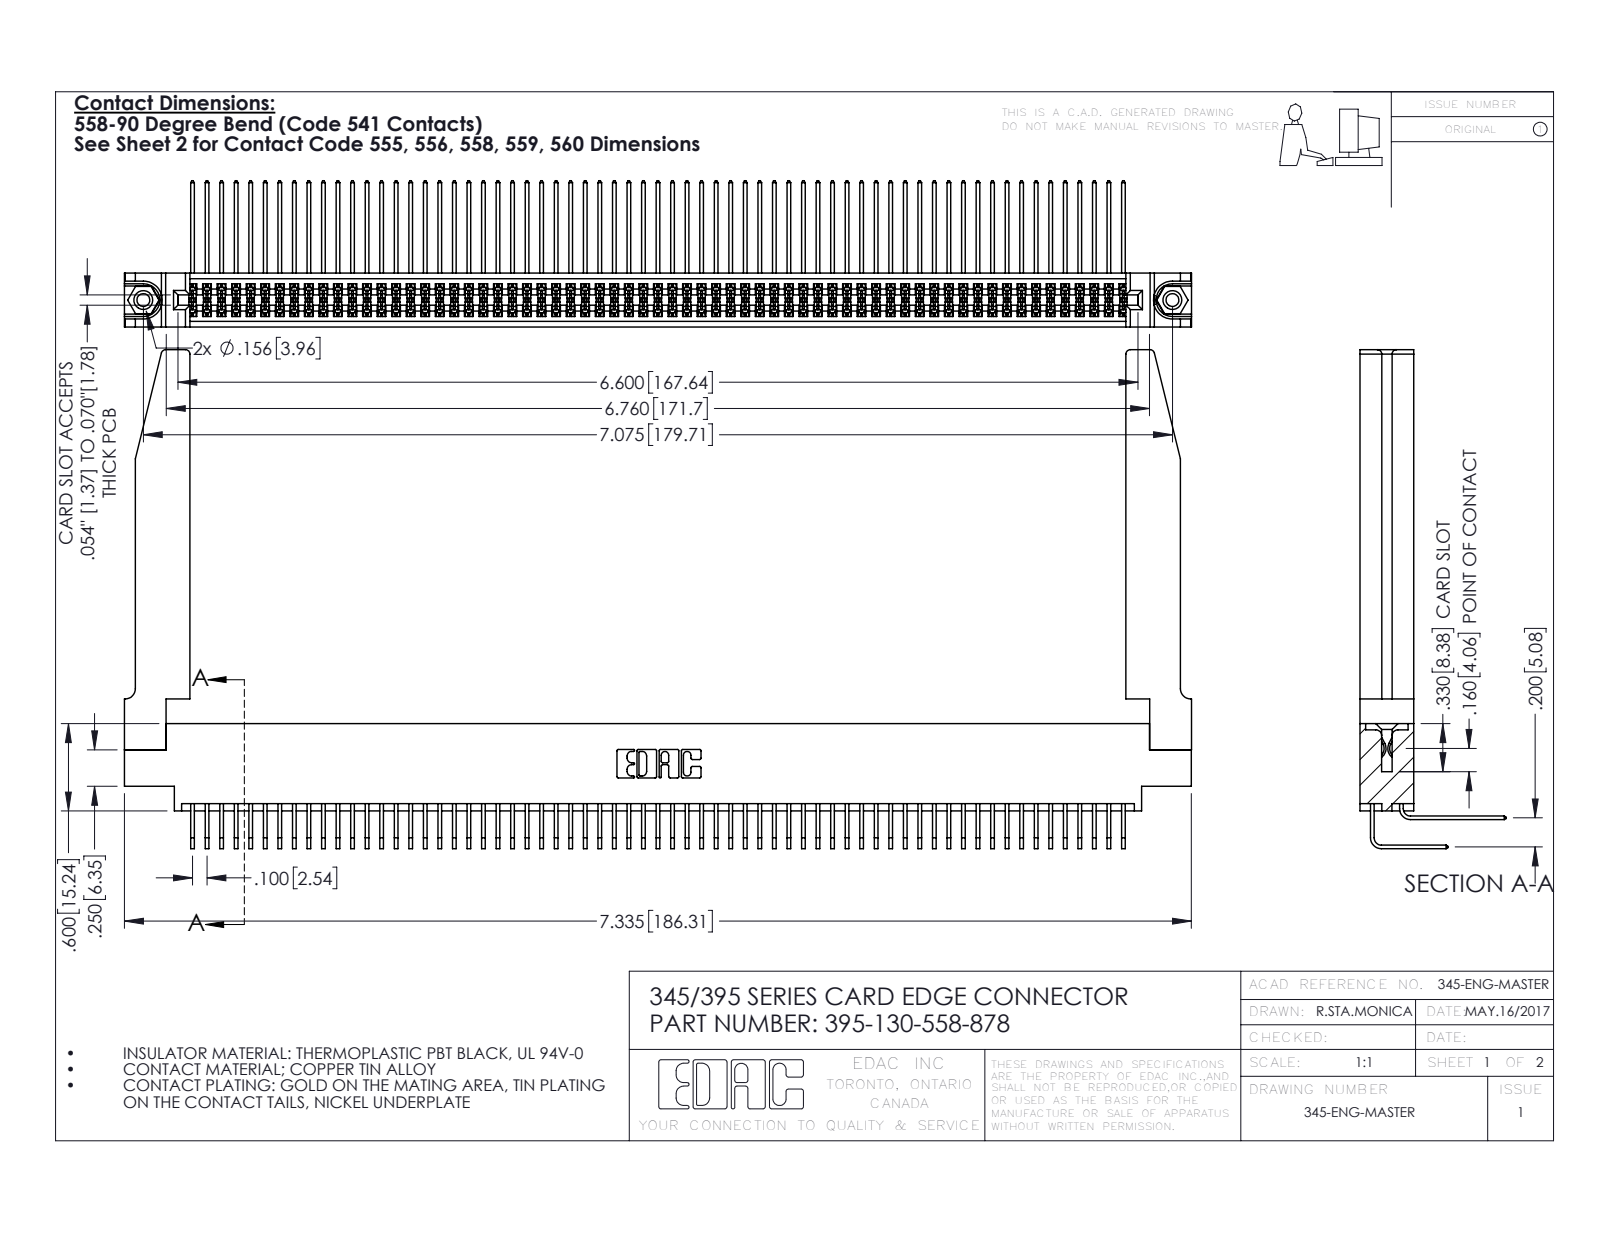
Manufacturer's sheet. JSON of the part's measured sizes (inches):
{"part_name": "345-292-001_558 559 Tail - 1; 345 Part_0.170 Offset - 0.156 Dia-TH; 395-130-558-878; 345-250-001_345-250-001-102 (+2 more)", "step_written_by": "SolidWorks 2016 (CONFIG_CONTROL_DESIGN)", "units": "inches", "bodies": {"solids": 135, "faces": 7124, "planar": 4776, "cylindrical": 2296, "other": 52}, "overall_size": [7.336, 3.429, 1.005], "volume_in3": 1.631, "surface_area_in2": 60.4, "round_holes": [[0.089, 2], [0.125, 2], [0.156, 2], [0.064, 1]], "round_bosses_or_shafts": [[0.155, 2]], "partial_cylinders_radius": [[0.006, 196], [0.01, 22], [0.03, 8], [0.007, 6], [0.031, 6], [0.026, 3], [0.014, 2], [0.019, 2]], "face_to_face_distances": [0.072, 0.298, 0.37, 0.2, 0.098, 0.272, 0.025, 0.225, 0.175, 0.025], "hole_center_spacings": [0.27, 6.839, 7.075]}
